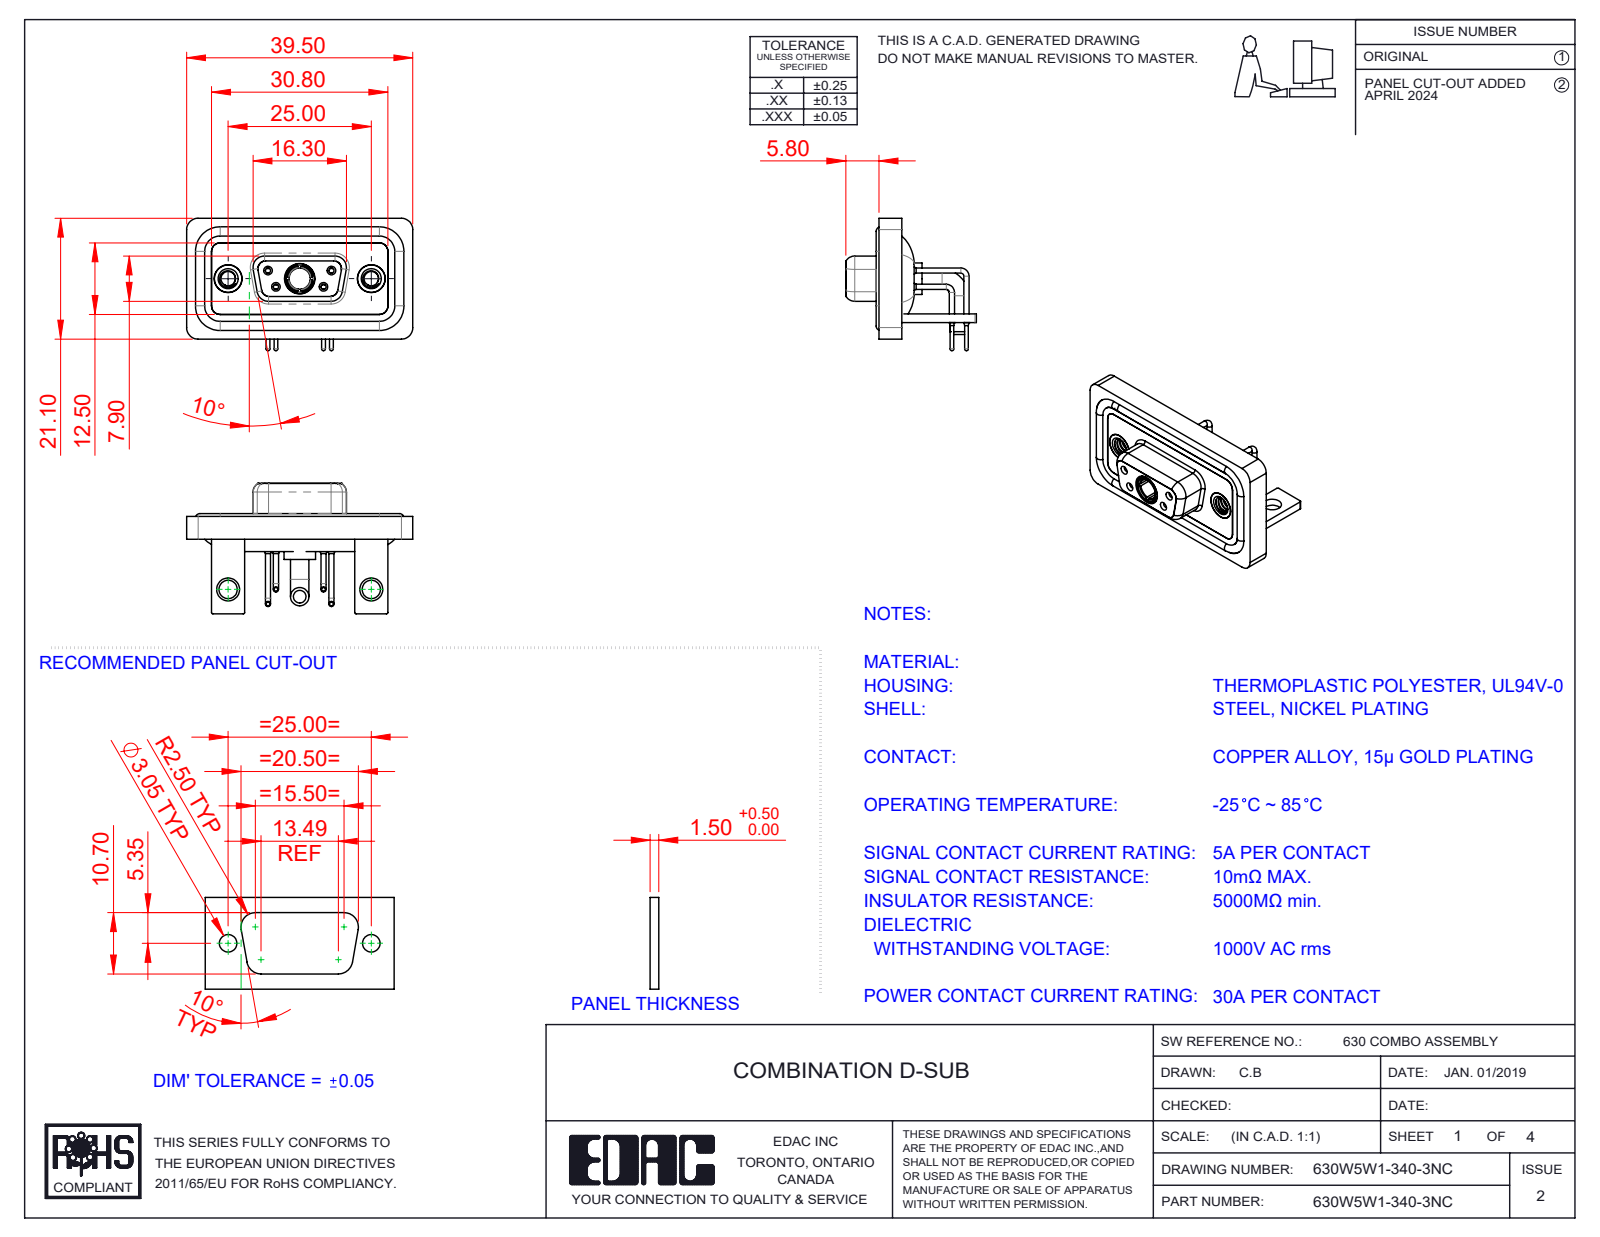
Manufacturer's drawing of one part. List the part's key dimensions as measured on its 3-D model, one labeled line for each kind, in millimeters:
Part name (STEP PRODUCT): 630Combo Threaded Rivet_A; 630Combo Contact Row 2_50 Contacts; Power Socket_30A RA; 630W5W1-340-3NC (+6 more)
STEP written by: SolidWorks 2023 (CONFIG_CONTROL_DESIGN)
Units: millimetres
Bodies: 15 solids, 718 faces (214 planar, 327 cylindrical, 177 other)
Overall size (bounding box): 39.5 × 23.12 × 22.8
Volume: 5 216 mm³ · Surface area: 8 600 mm²
Round holes (diameter × count): ⌀0.9 ×4, ⌀1.1 ×4, ⌀1.5 ×4, ⌀2 ×4, ⌀4.85 ×3, ⌀1.6 ×2, ⌀1.7 ×2, ⌀2.5 ×2, ⌀3.2 ×2, ⌀4 ×2, ⌀4.05 ×2, ⌀5 ×2
Round bosses / shafts (diameter × count): ⌀1.6 ×6, ⌀0.9 ×4, ⌀0.65 ×4, ⌀4.95 ×2, ⌀4.8 ×2, ⌀3.2 ×2, ⌀5.5 ×1, ⌀5.2 ×1
Partial cylindrical surfaces — rounded edges, fillets, slot ends (radius × count): R2 ×19, R1.5 ×18, R0.25 ×16, R1.35 ×8, R1.6 ×8, R0.5 ×5, R0.6 ×4, R0.65 ×4
Main face-to-face distances: 0.4, 2.9, 1.5, 1.8, 1.1, 3.7, 1.6, 0.8, 2.5, 3.1
Hole centre spacings: 3.16, 5.72, 7.1, 12.5, 18.1, 25, 4.39, 4.4
